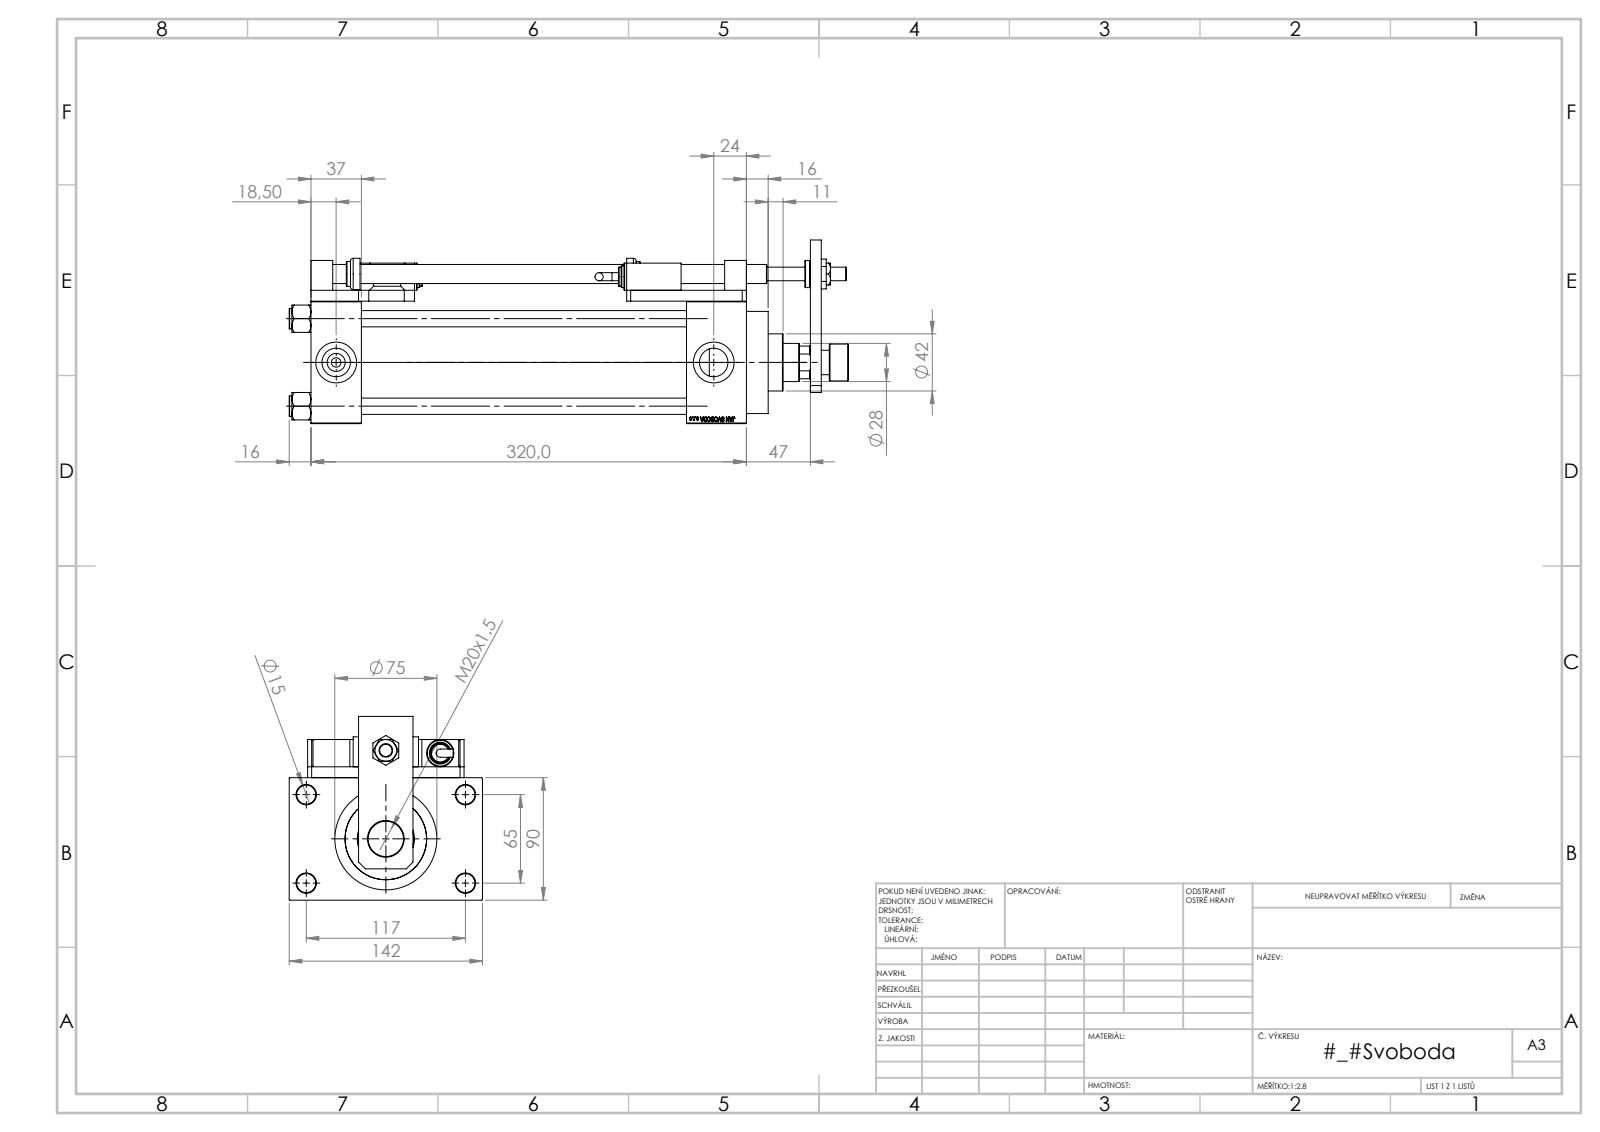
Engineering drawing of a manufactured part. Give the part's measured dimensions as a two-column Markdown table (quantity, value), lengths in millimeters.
| quantity | value |
| --- | --- |
| part name | V215CD_SWITCH_Q_DIMA; V215CD_VCP_D; V215CD_SWITCH_Q_SWITCH; V215CR_ROD_END_F (+7 more) |
| STEP written by | SolidWorks 2019 (CONFIG_CONTROL_DESIGN) |
| units | millimeters |
| bodies | 25 solids, 1345 faces (622 planar, 160 cylindrical, 563 other) |
| overall size | 411 × 142 × 135 |
| volume | 1 705 000 mm³ |
| surface area | 414 349 mm² |
| round holes (diameter × count) | 14 × 5, 8.5 × 4, 12 × 4, 13.5 × 4, 7 × 2, 20.96 × 2, 30 × 2, 10 × 1, 18.5 × 1, 20 × 1, 28 × 1, 31 × 1 |
| round bosses / shafts (diameter × count) | 15 × 4, 20 × 3, 16 × 2, 14 × 2, 6 × 2, 75 × 1, 69 × 1, 42 × 1 |
| partial cylindrical surfaces (radius × count) | 7.5 × 4 |
| main face-to-face distances | 8, 90, 44, 320, 37, 98, 283, 276, 239, 47 |
| hole center spacings | 66.92, 26.35, 45.47, 64.3, 69.81, 90.65, 111.34, 65 |
